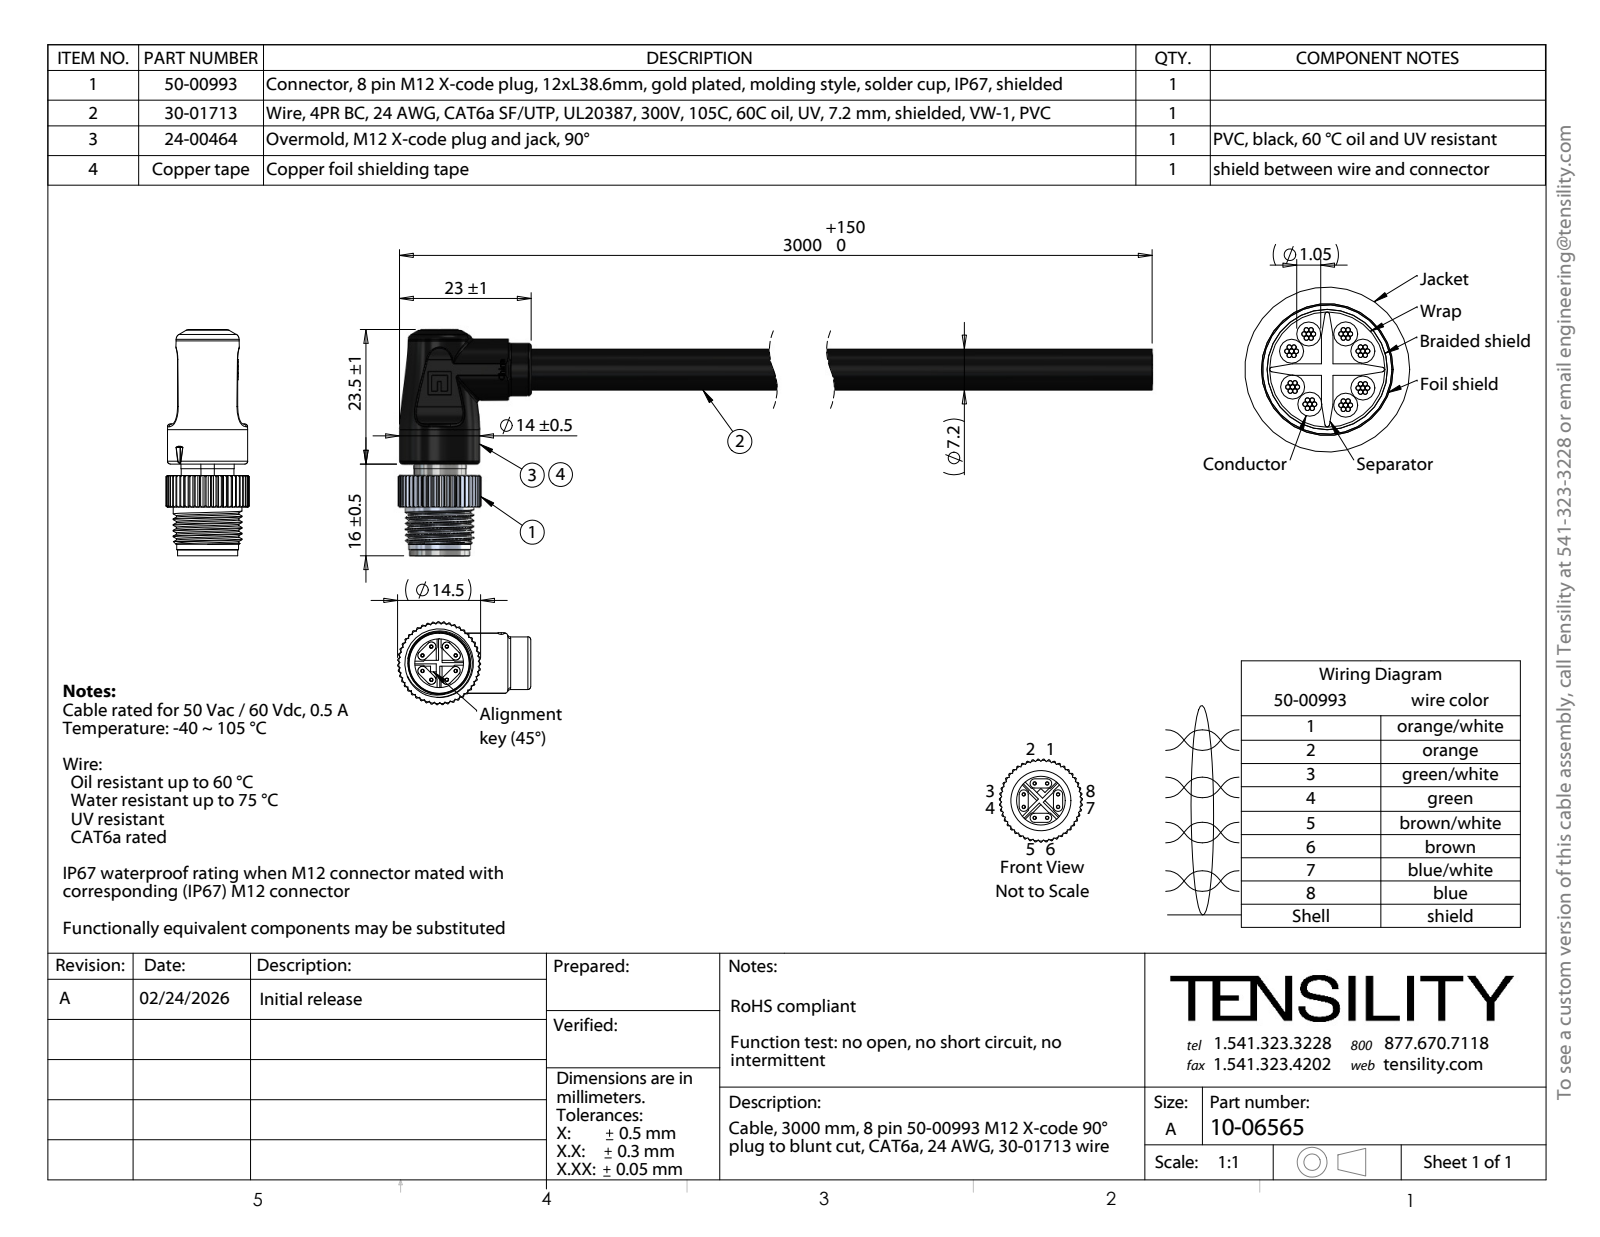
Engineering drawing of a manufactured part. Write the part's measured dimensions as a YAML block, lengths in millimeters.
part_name: "10-06565; 50-00993-02; 50-00993_STEP; 50-00993-03 (+5 more)"
step_written_by: "SolidWorks 2025 (CONFIG_CONTROL_DESIGN)"
units: millimeters
bodies: {solids: 85, faces: 1492, planar: 552, cylindrical: 617, other: 323}
overall_size: [173.25, 39.5, 14.49]
volume: 10489
surface_area: 46188
round_holes:
  - {diameter: 0.2, count: 56}
  - {diameter: 0.6, count: 8}
  - {diameter: 1.2, count: 8}
  - {diameter: 2, count: 1}
  - {diameter: 2.5, count: 1}
  - {diameter: 5.03, count: 1}
  - {diameter: 5.25, count: 1}
  - {diameter: 5.65, count: 1}
  - {diameter: 5.75, count: 1}
  - {diameter: 7.5, count: 1}
  - {diameter: 8.5, count: 1}
  - {diameter: 9.07, count: 1}
round_bosses_or_shafts:
  - {diameter: 1.4, count: 8}
  - {diameter: 1.15, count: 8}
  - {diameter: 1.05, count: 8}
  - {diameter: 0.8, count: 8}
  - {diameter: 9.2, count: 2}
  - {diameter: 14, count: 1}
  - {diameter: 12, count: 1}
  - {diameter: 11, count: 1}
partial_cylinders:
  - {radius: 0.1, count: 12}
  - {radius: 0.8, count: 8}
  - {radius: 1, count: 8}
  - {radius: 0.5, count: 6}
  - {radius: 2.17, count: 4}
  - {radius: 7.25, count: 1}
face_to_face_distances: [0.5, 2, 0.99, 0.98, 6, 5.5, 5, 16.25, 16.75, 0.7]
hole_center_spacings: [0.35, 1.61, 1.78, 3.19, 0.41, 1.06, 1.43, 1.93]
